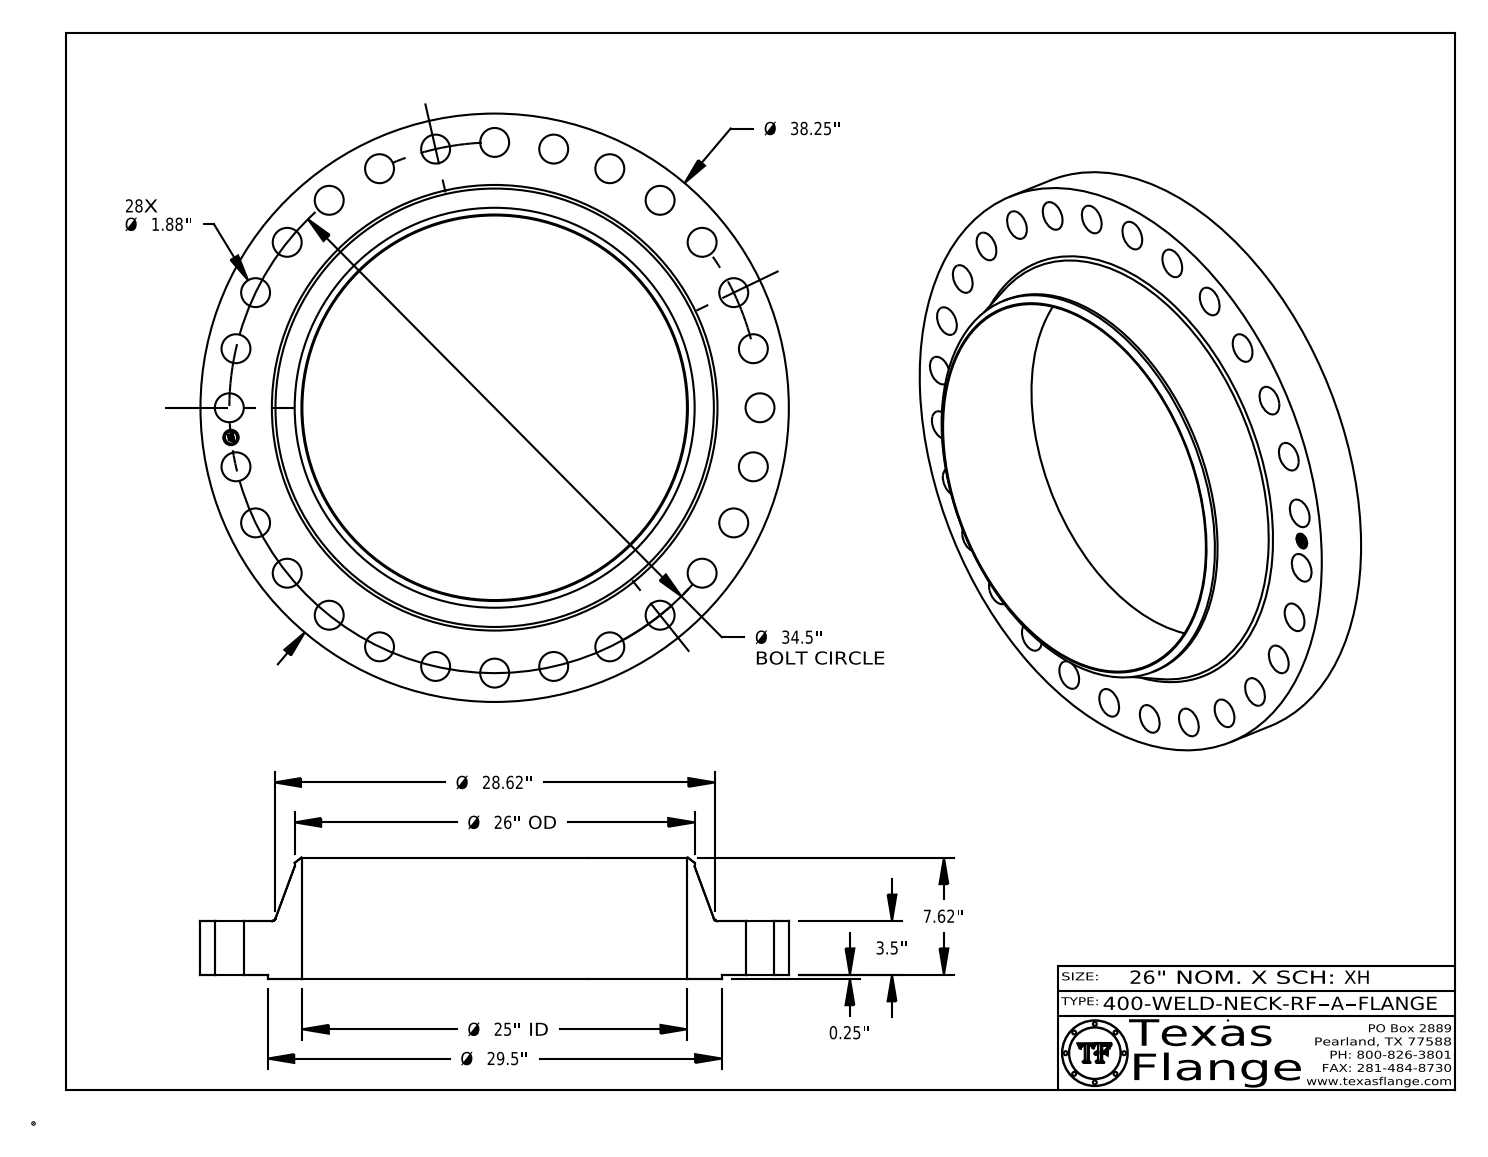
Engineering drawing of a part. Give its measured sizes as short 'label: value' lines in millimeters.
name: 400-WELD-NECK-RF, Series A
written by: CATIA V5 STEP AP214 (AUTOMOTIVE_DESIGN)
unit: mm
bodies: 1 solid, 459 faces (369 planar, 84 cylindrical, 6 other)
size: 971.6 × 971.6 × 199.9
volume: 39 920 000 mm³; area: 1 960 000 mm²
holes: 28× ⌀47.8, 1× ⌀25.4, 1× ⌀635
bosses: 8× ⌀1.5, 1× ⌀971.6, 1× ⌀749.3, 1× ⌀660.4, 1× ⌀20
face distances: 88.9, 6.4, 95.3, 199.9, 193.5, 104.6, 0.4, 94.9, 88.5, 105
hole spacings: 438.2, 685.1, 870.8, 380.2, 466.2, 827.1, 854.3, 289.4
